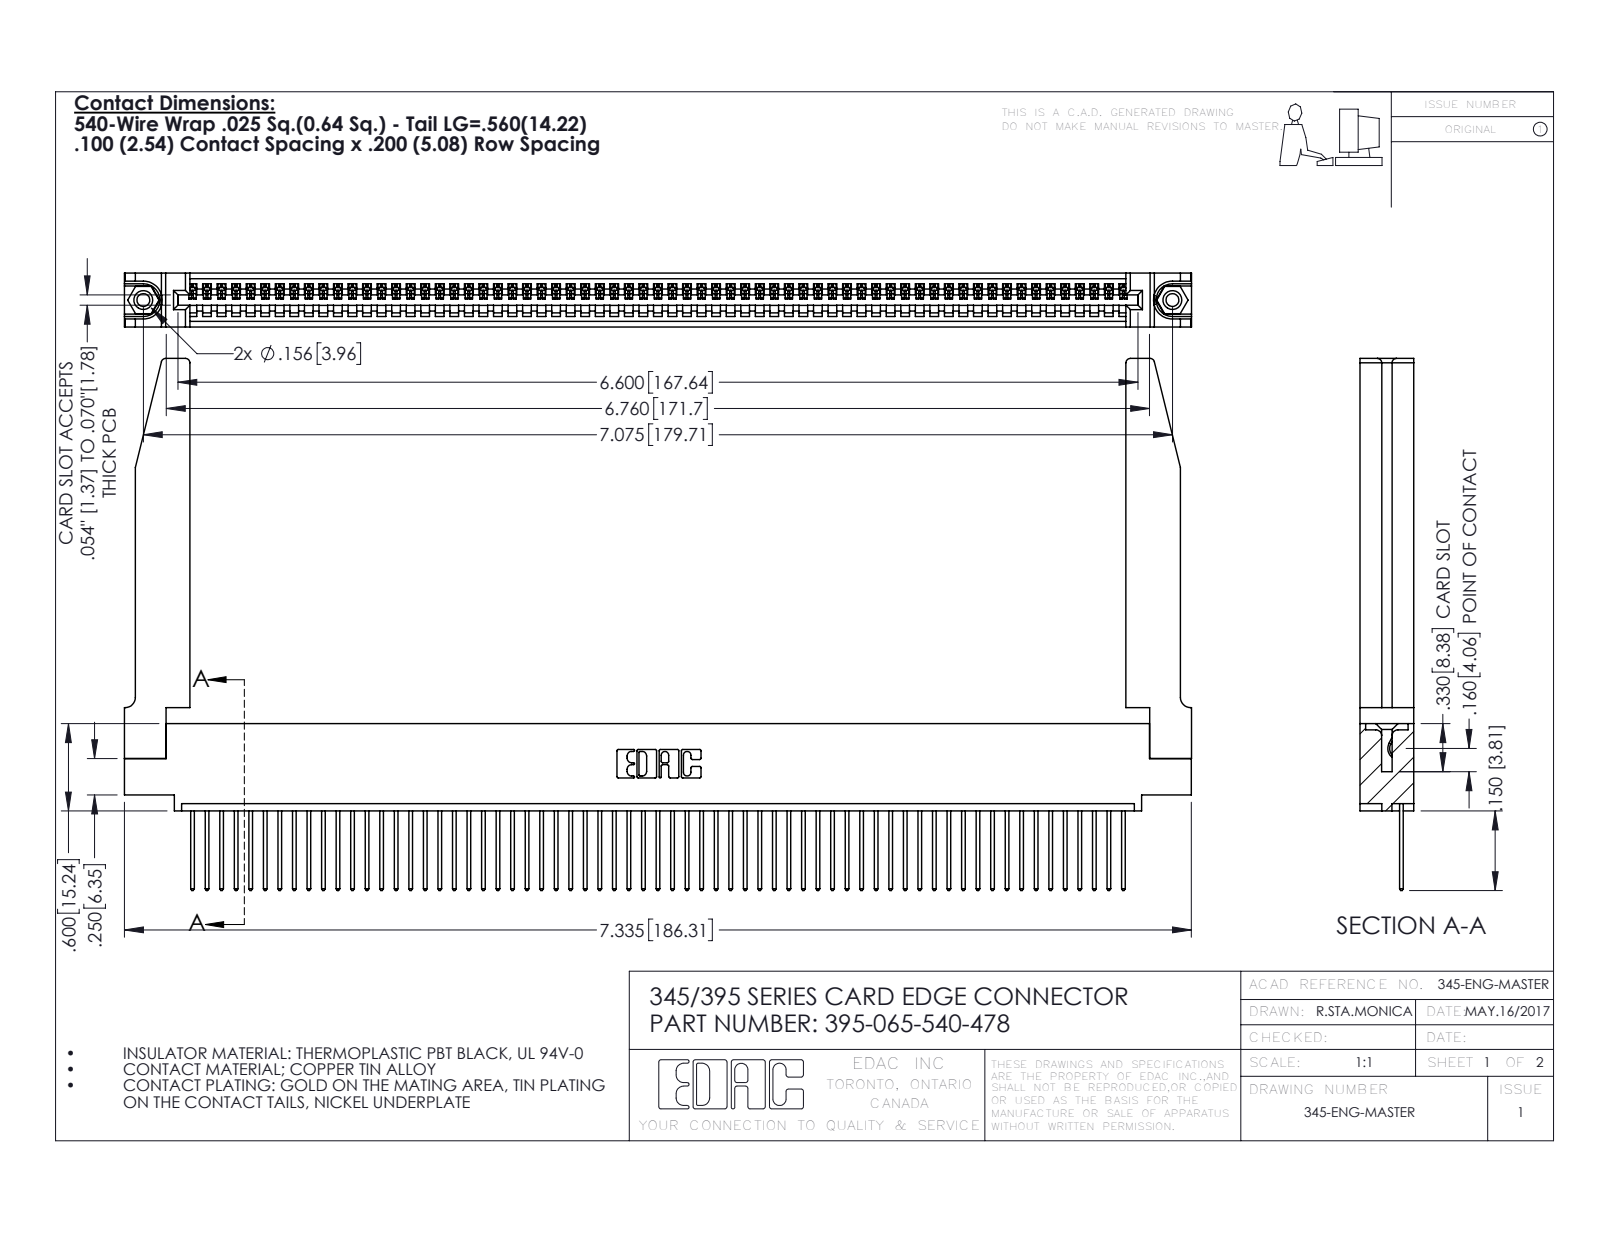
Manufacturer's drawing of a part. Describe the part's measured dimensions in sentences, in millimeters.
The part is named "345 Part_0.110 Offset - 0.156 Dia-TH; 395-065-540-478; 345-220-078_345-220-078; 345-292-001_345-293-140 (+1 more)". Its 3-D file was written by "SolidWorks 2016 (CONFIG_CONTROL_DESIGN)". It is 70 solids with 4134 faces: 2826 planar, 1256 cylindrical and 52 other. Overall it measures 186.3 by 92.9 by 9.4 millimeters. Its volume is 25 680 cubic millimeters and its surface area 31 660 square millimeters. Round holes: 2 of diameter 2.3, 2 of diameter 3.2, 2 of diameter 4, 1 of diameter 1.6. Round bosses or shafts: 2 of diameter 3.9. Partial cylindrical surfaces (rounded edges, fillets, slot ends): 130 of radius 0.2, 130 of radius 0.3, 22 of radius 0.3, 8 of radius 0.8, 6 of radius 0.2, 6 of radius 0.8, 3 of radius 0.7, 2 of radius 0.8. The main face-to-face distances are 1.8, 7.6, 9.4, 2.5, 6.9, 0.6, 5.1, 5.7, 3.8, 3.8. The hole center spacings are 6.9, 173.7, 179.7.
